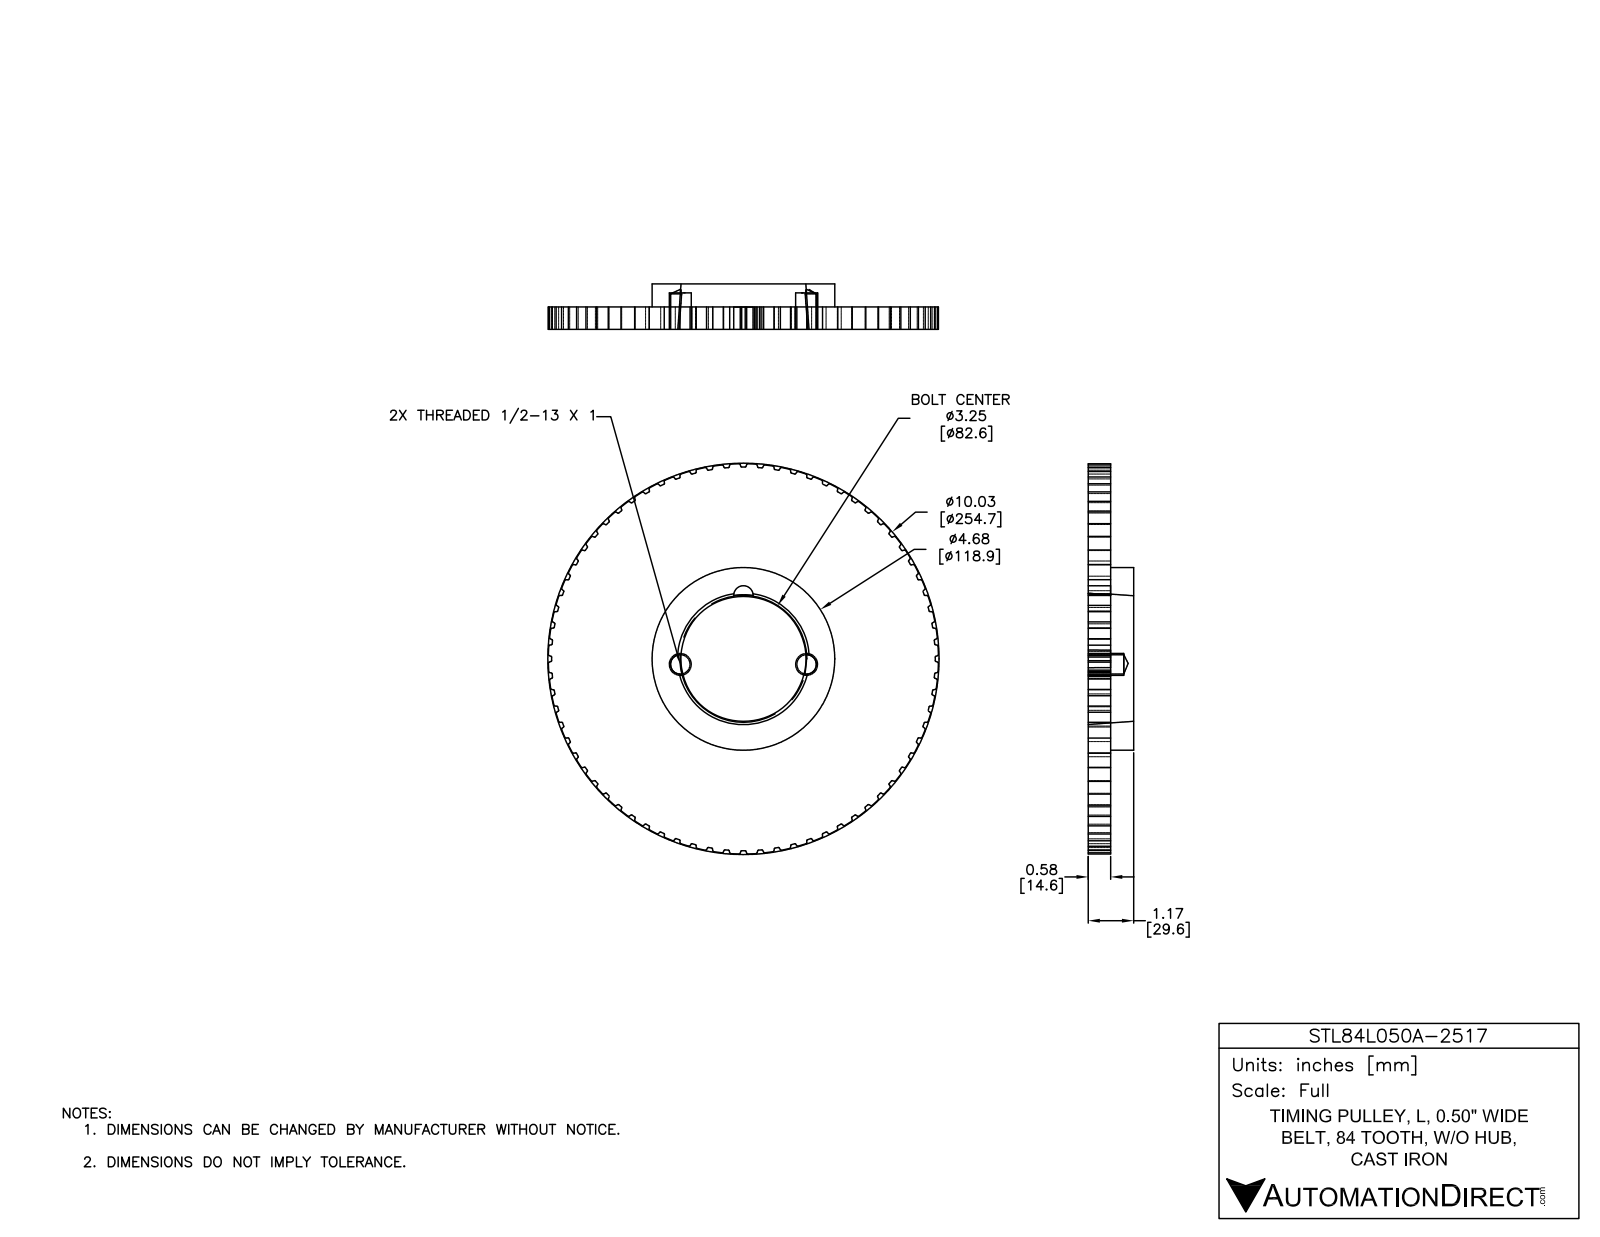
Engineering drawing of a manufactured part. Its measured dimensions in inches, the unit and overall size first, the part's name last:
Units: inches
Overall size (bounding box): 10 × 10 × 1.165
Round bosses / shafts (diameter × count): ⌀4.68 ×1, ⌀4.68 ×1
Partial cylindrical surfaces — rounded edges, fillets, slot ends (radius × count): R0.015 ×168, R0.02 ×168, R0.185 ×2, R0.225 ×1, R5 ×1
Main face-to-face distances: 0.575, 0.294, 0.869, 1.165, 0.87, 0.295, 3.255, 9.838, 3.254, 9.84
Volume: 44.58 in³ · Surface area: 182.4 in²
Bodies: 1 solid, 756 faces (257 planar, 497 cylindrical, 2 other)
Part name (STEP PRODUCT): STL84L050A-2517
STEP written by: SolidWorks 2015 (AUTOMOTIVE_DESIGN)
